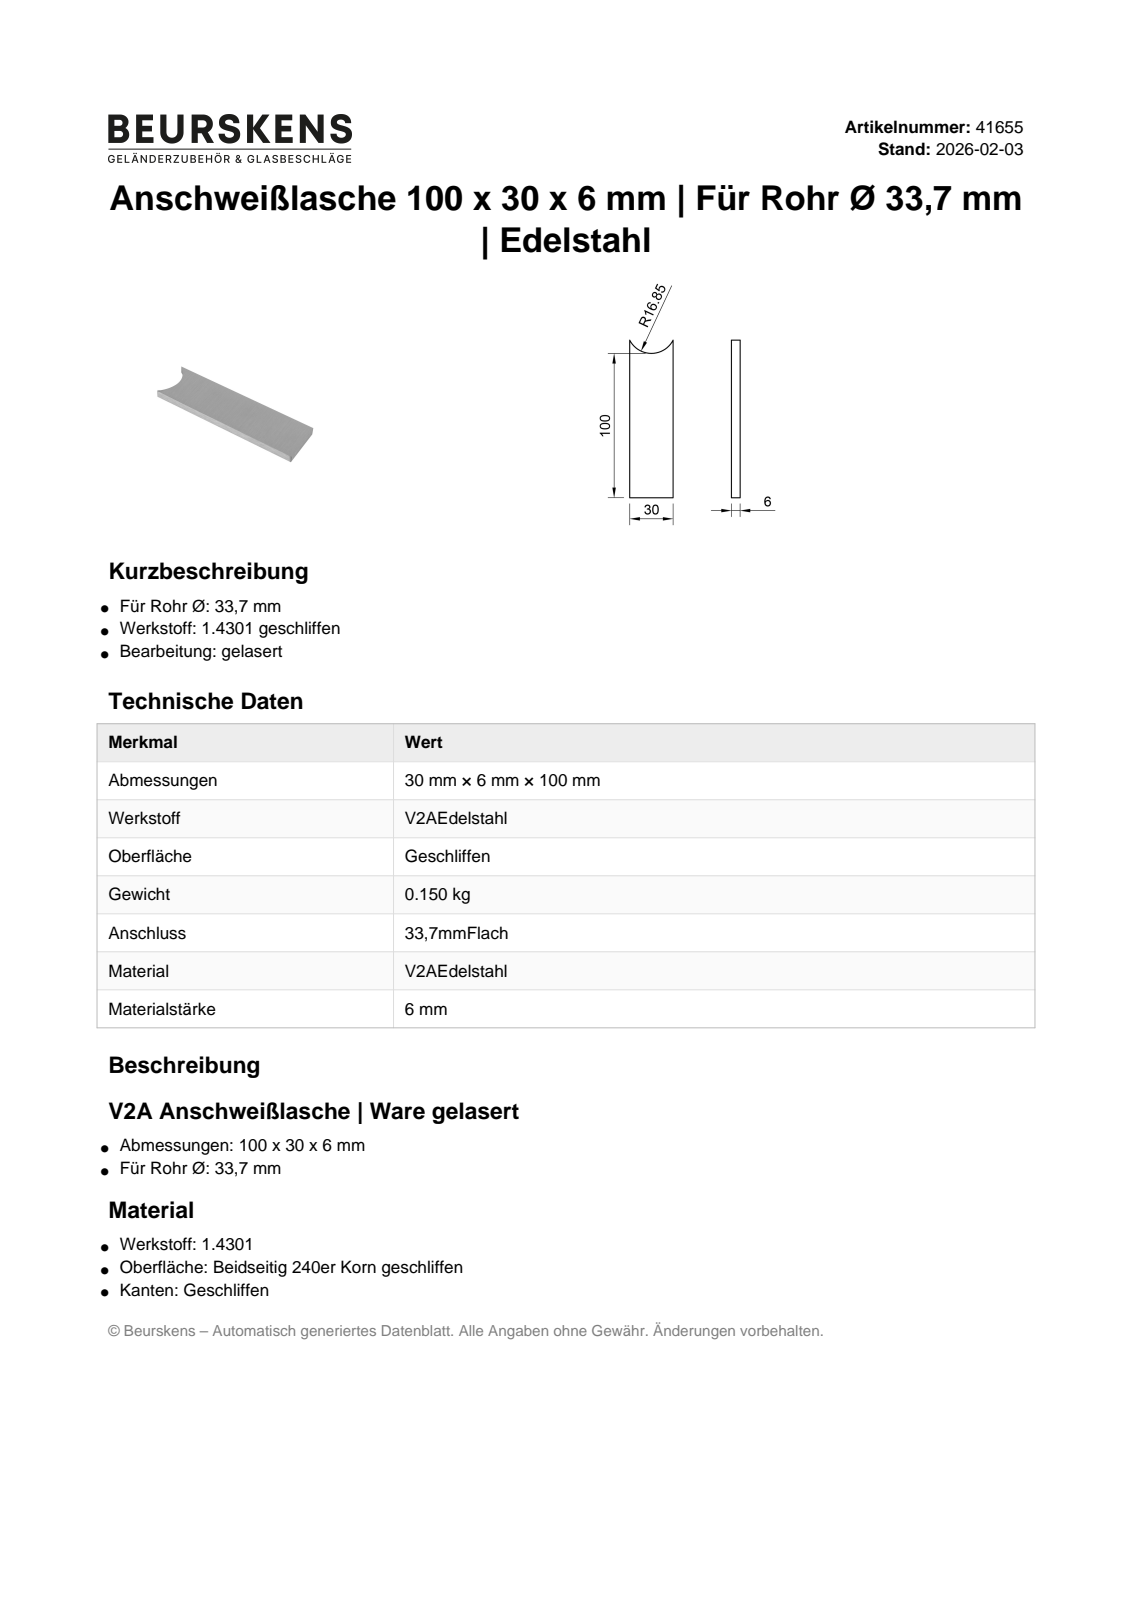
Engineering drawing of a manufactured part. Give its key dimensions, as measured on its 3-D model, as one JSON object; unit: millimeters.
{"part_name": "41655", "step_written_by": "Autodesk Inventor 2022 (AUTOMOTIVE_DESIGN)", "units": "millimeters", "bodies": {"solids": 1, "faces": 6, "planar": 5, "cylindrical": 1, "other": 0}, "overall_size": [100, 30, 6], "volume_mm3": 16821, "surface_area_mm2": 7209, "partial_cylinders_radius": [[16.85, 1]], "face_to_face_distances": [6, 30]}
